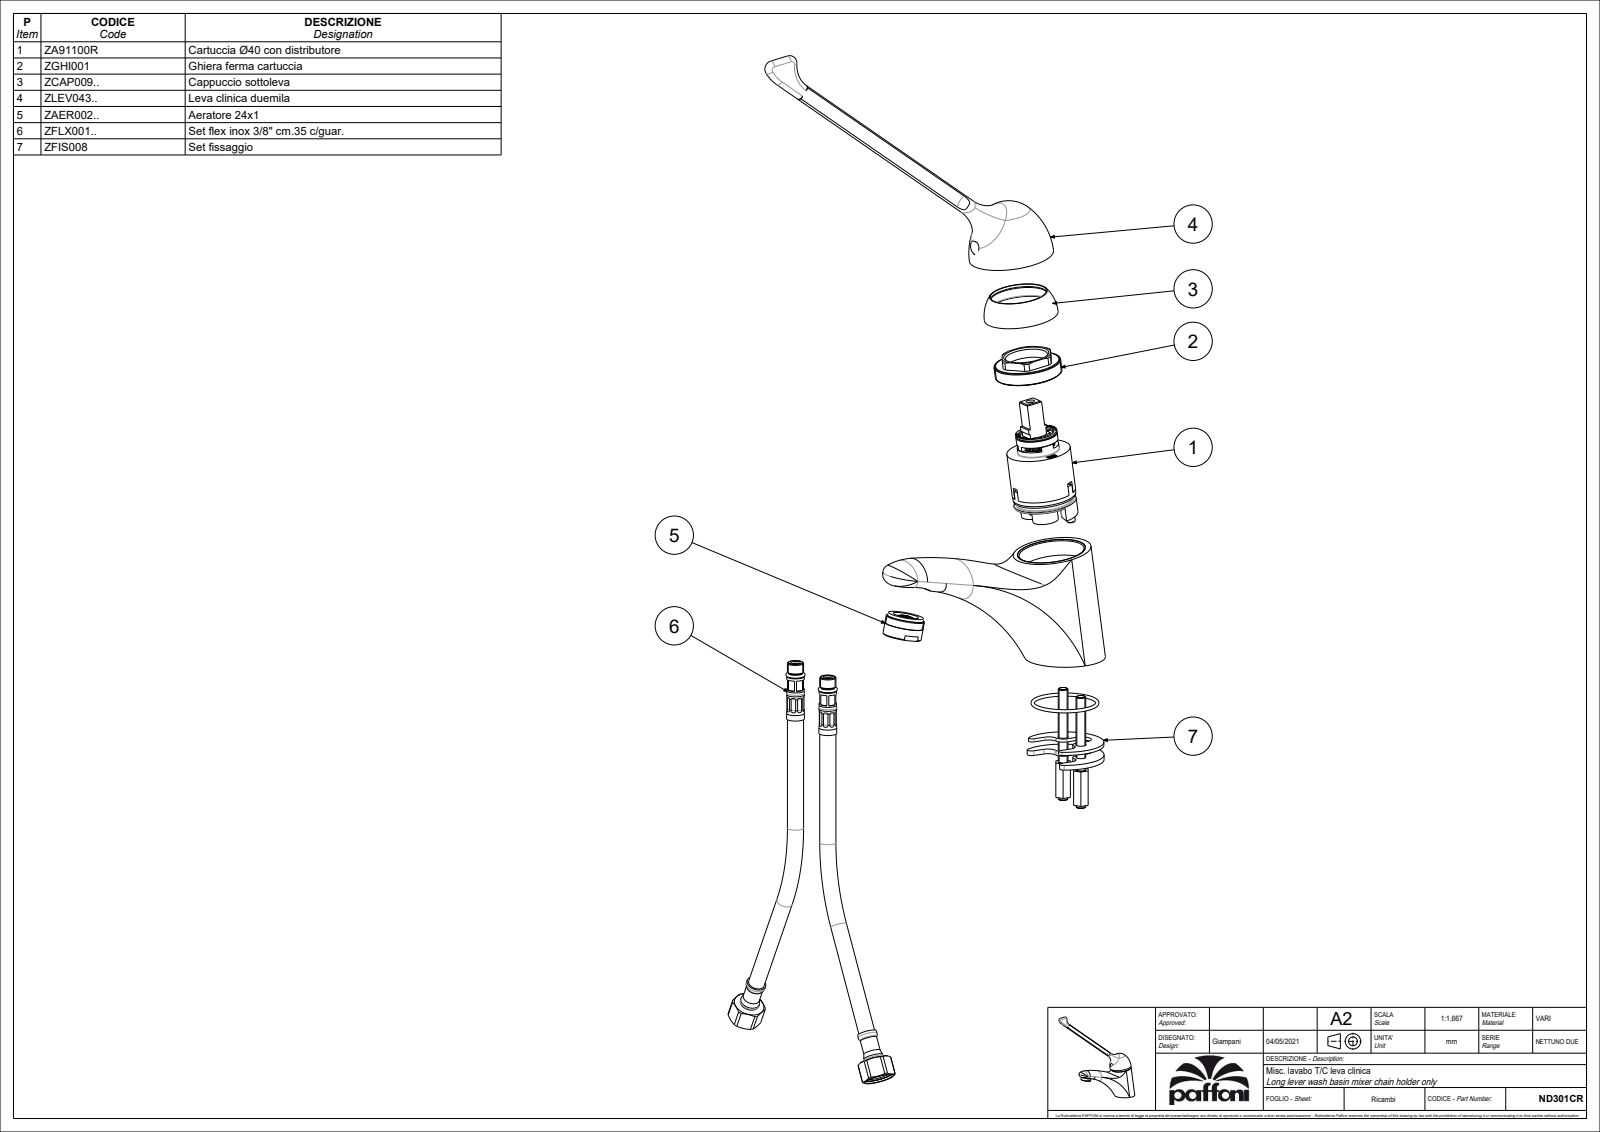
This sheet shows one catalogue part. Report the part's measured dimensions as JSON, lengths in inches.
{"part_name": "ND301CR", "step_written_by": "CREO PARAMETRIC BY PTC INC, 2020044 (CONFIG_CONTROL_DESIGN)", "units": "inches", "bodies": {"solids": 1, "faces": 188, "planar": 49, "cylindrical": 57, "other": 82}, "overall_size": [8.78, 8.366, 2.067], "volume_in3": 11.93, "surface_area_in2": 89.44, "round_holes": [[0.197, 3], [0.217, 2], [0.276, 2], [0.354, 2], [0.433, 2], [1.594, 2], [0.236, 1], [0.965, 1], [1.378, 1], [1.539, 1], [1.673, 1]], "round_bosses_or_shafts": [[1.476, 1], [0.945, 1], [0.394, 1], [0.315, 1]], "partial_cylinders_radius": [[0.118, 2], [0.157, 1]], "face_to_face_distances": [0.236, 2.027, 2.029, 0.189, 0.425, 0.315, 0.551, 0.079, 0.11, 0.504], "hole_center_spacings": [0.339, 0.615, 0.338, 0.452, 0.465, 0.53, 0.615, 0.622]}
